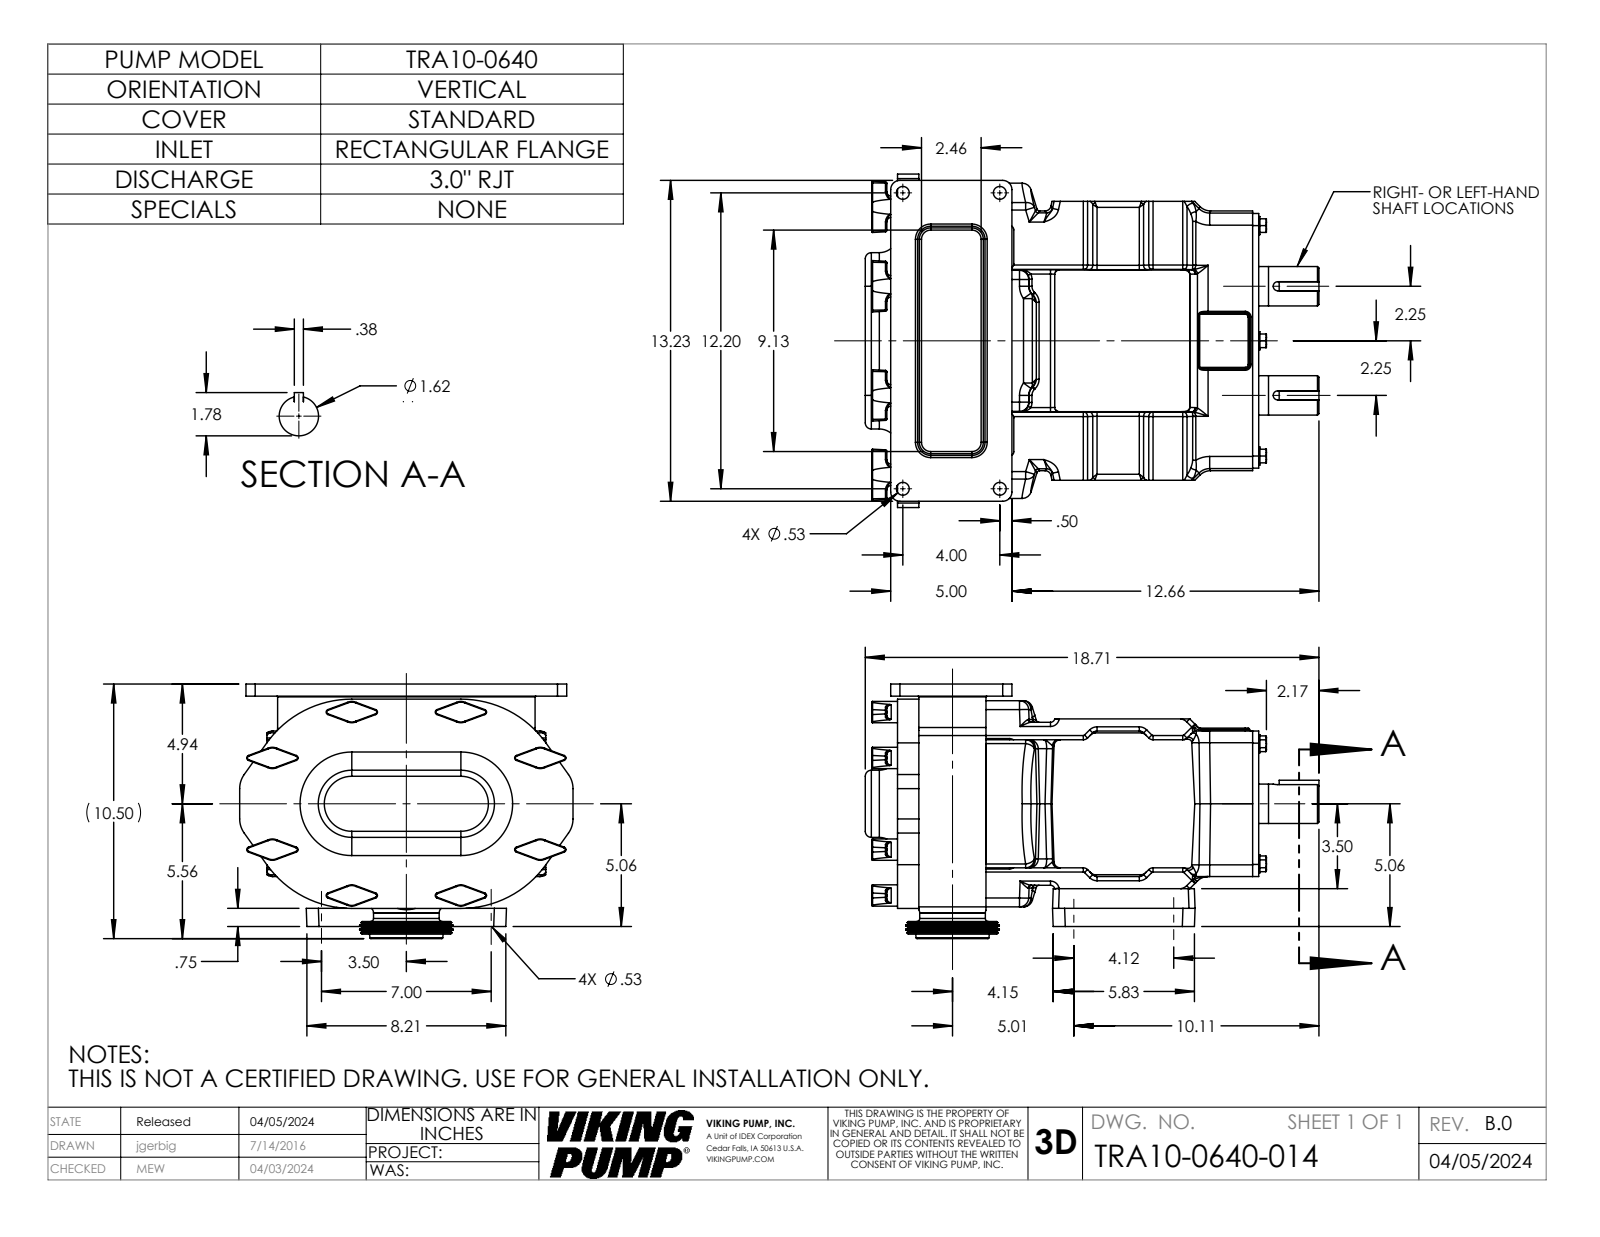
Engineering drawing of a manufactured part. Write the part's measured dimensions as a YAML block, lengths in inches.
part_name: "0600RJT30; TRA10-0600-COVER-STD; TRA10-0600-GEARBOX-V; TRA10-0640-014 (+1 more)"
step_written_by: "SolidWorks 2022 (AUTOMOTIVE_DESIGN)"
units: inches
bodies: {solids: 4, faces: 1105, planar: 292, cylindrical: 393, other: 420}
overall_size: [18.714, 13.75, 10.497]
volume: 1230
surface_area: 1441
round_holes:
  - {diameter: 0.531, count: 8}
  - {diameter: 2.368, count: 1}
  - {diameter: 2.844, count: 1}
  - {diameter: 3.563, count: 1}
round_bosses_or_shafts:
  - {diameter: 0.88, count: 8}
  - {diameter: 0.75, count: 6}
  - {diameter: 1.624, count: 2}
  - {diameter: 2.708, count: 1}
partial_cylinders:
  - {radius: 0.18, count: 44}
  - {radius: 0.06, count: 43}
  - {radius: 0.03, count: 36}
  - {radius: 0.38, count: 36}
  - {radius: 0.25, count: 32}
  - {radius: 0.12, count: 24}
  - {radius: 0.5, count: 22}
  - {radius: 0.09, count: 16}
face_to_face_distances: [2.769, 0.5, 0.88, 3.649, 1.437, 0.36, 11.25, 14.899, 14.019, 5.64]
hole_center_spacings: [4, 4.012, 4.12, 6.107, 6.404, 6.435, 7, 7.519]
